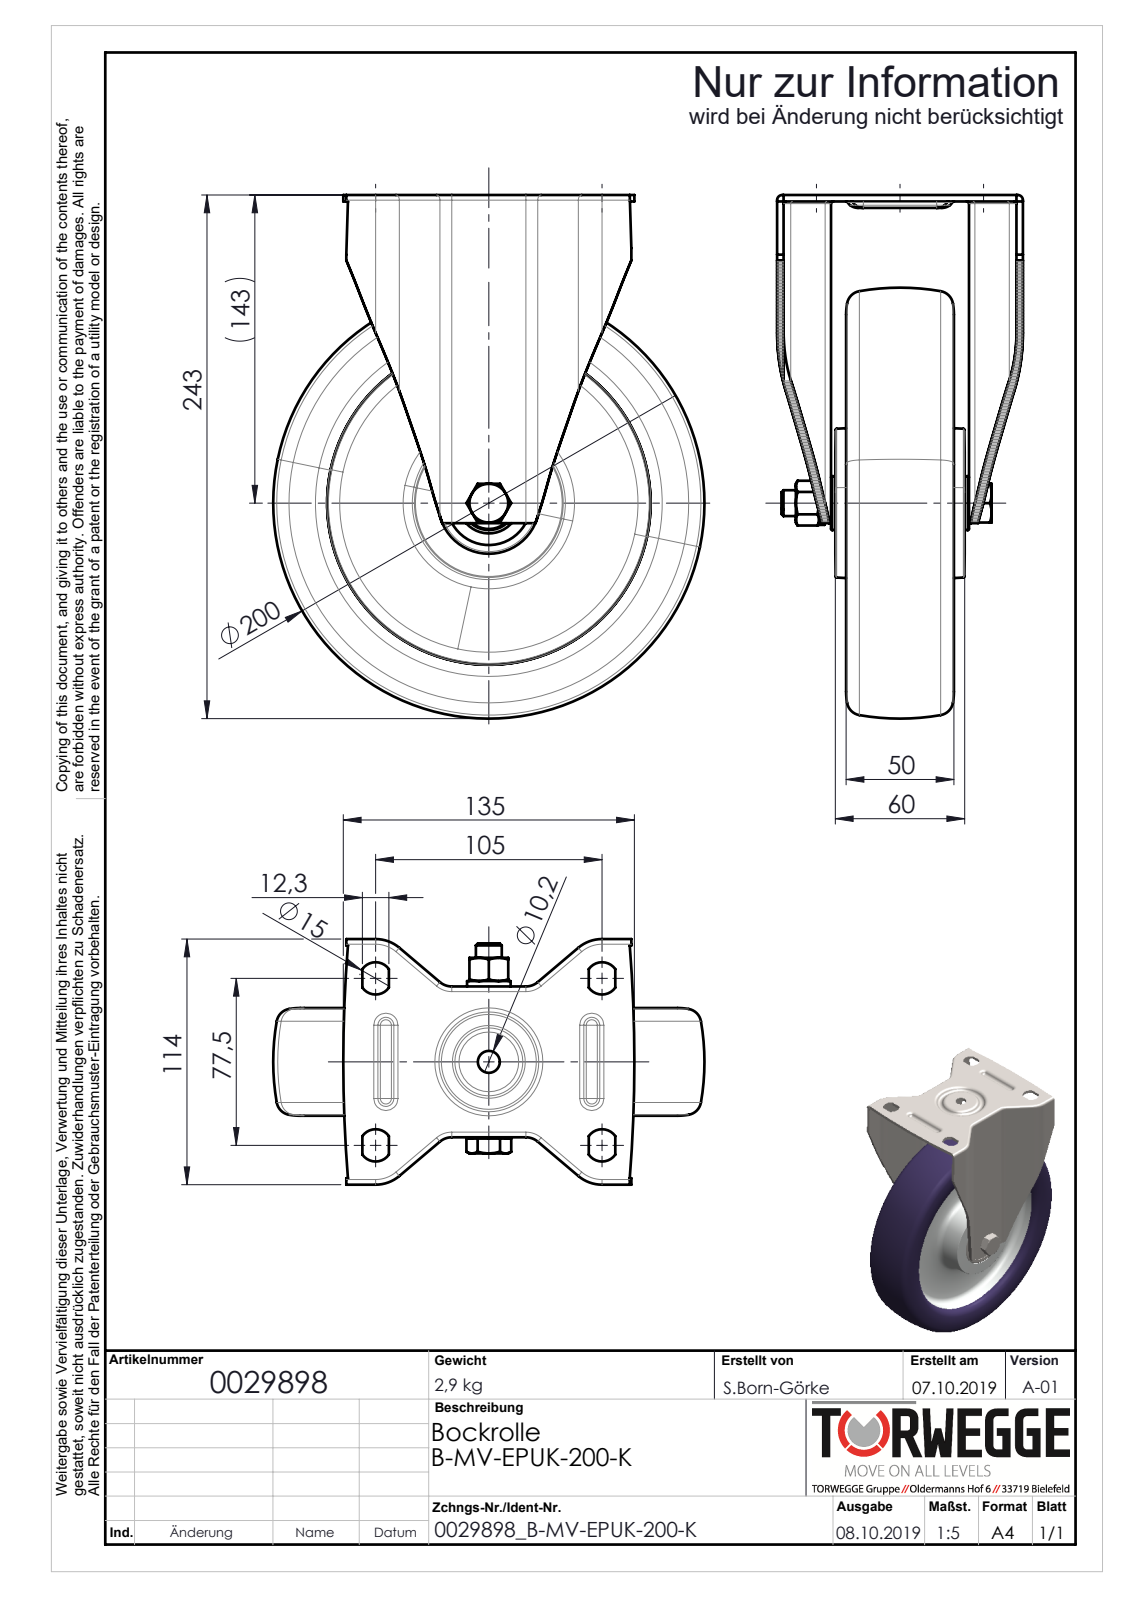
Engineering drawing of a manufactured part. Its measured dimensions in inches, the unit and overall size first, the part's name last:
Units: inches
Overall size (bounding box): 9.503 × 7.874 × 4.488
Round holes (diameter × count): ⌀0.402 ×2, ⌀0.472 ×1, ⌀0.48 ×1, ⌀0.492 ×1, ⌀0.787 ×1, ⌀0.827 ×1, ⌀1.378 ×1, ⌀1.531 ×1
Round bosses / shafts (diameter × count): ⌀1.85 ×1, ⌀1.106 ×1, ⌀0.984 ×1, ⌀0.795 ×1, ⌀0.783 ×1, ⌀0.709 ×1
Partial cylindrical surfaces — rounded edges, fillets, slot ends (radius × count): R0.039 ×12, R0.094 ×8, R0.157 ×8, R0.118 ×6, R0.295 ×4, R0.335 ×4, R0.453 ×4, R0.551 ×4
Main face-to-face distances: 0.118, 0.95, 2.638, 2.52, 2.756, 0.689, 2.067, 0.571, 1.949, 1.068
Volume: 70.3 in³ · Surface area: 516.5 in²
Bodies: 11 solids, 1234 faces (852 planar, 153 cylindrical, 229 other)
Part name (STEP PRODUCT): 0029898_B-MV-EPUK-200-K_(A-01)
STEP written by: SolidWorks 2018 (AUTOMOTIVE_DESIGN)
